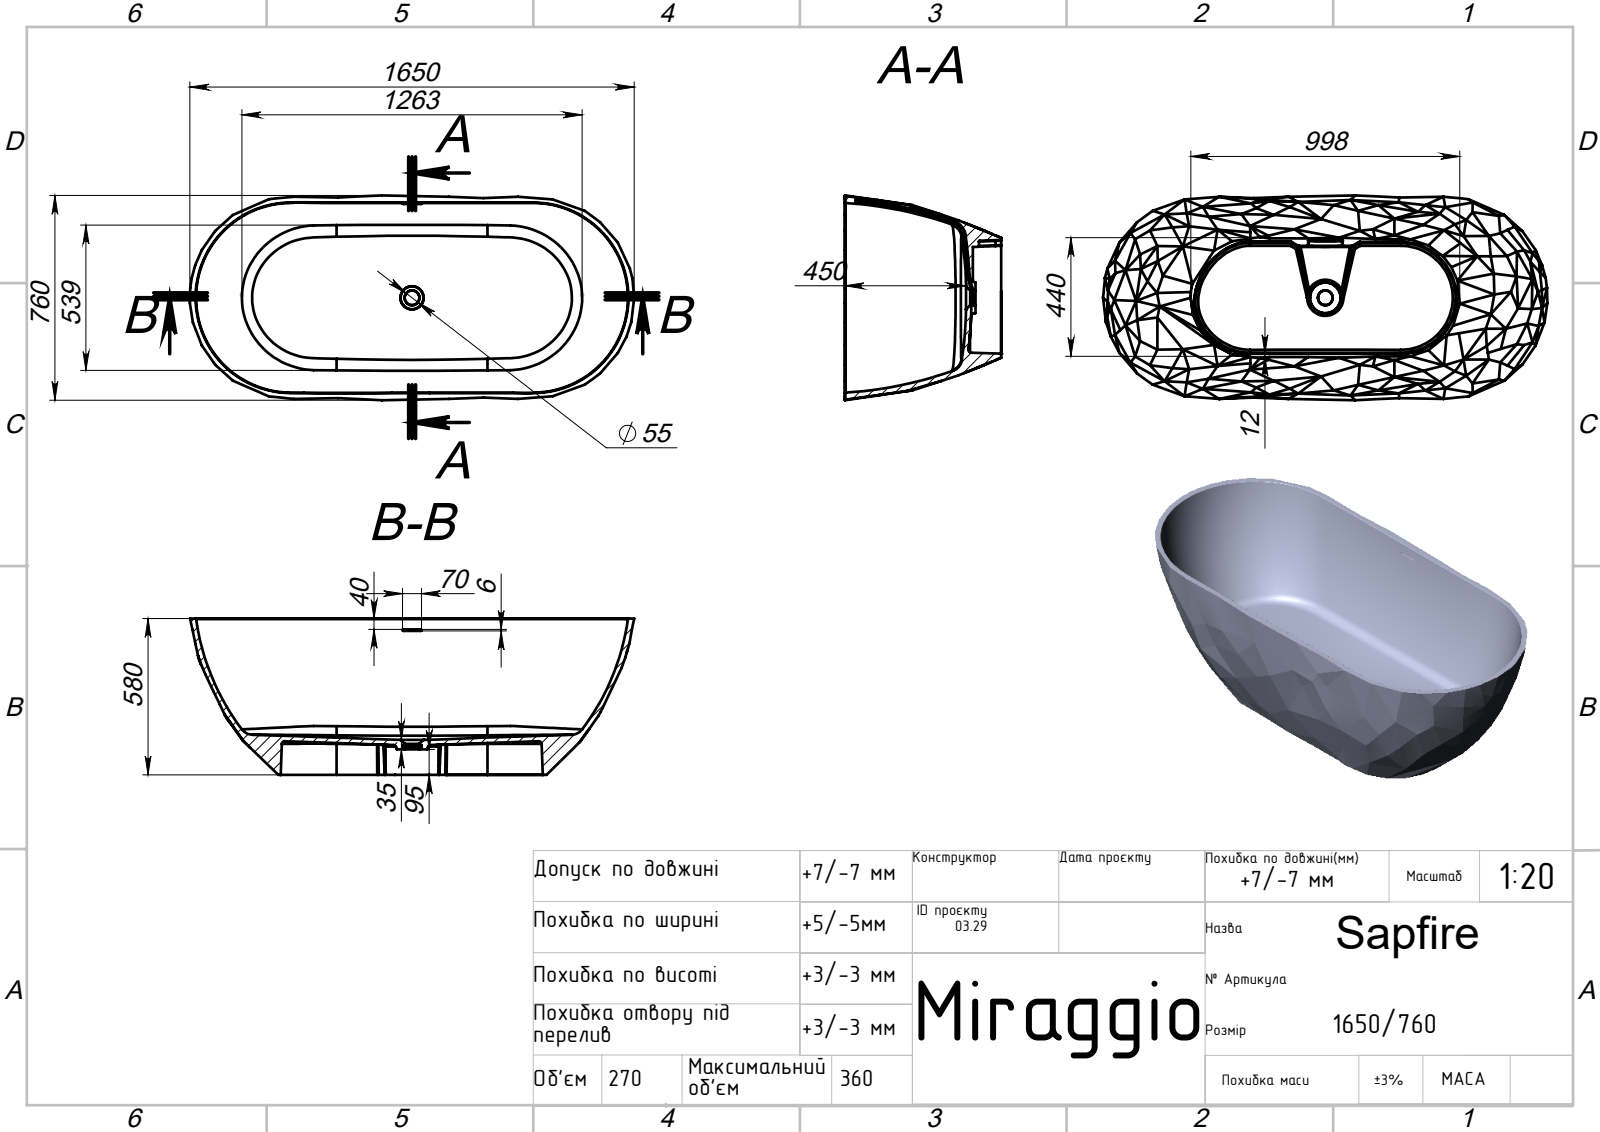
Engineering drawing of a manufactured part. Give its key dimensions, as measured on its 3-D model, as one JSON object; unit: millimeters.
{"part_name": "Sapfire", "step_written_by": "SolidWorks 2020 (AUTOMOTIVE_DESIGN)", "units": "millimeters", "bodies": {"solids": 1, "faces": 383, "planar": 234, "cylindrical": 20, "other": 129}, "overall_size": [1649.47, 760, 580], "volume_mm3": 63920000, "surface_area_mm2": 5275000, "round_holes": [[55, 1]], "partial_cylinders_radius": [[3, 6], [10, 6], [57, 1], [62.5, 1], [64, 1], [331.21, 1], [343.83, 1]], "face_to_face_distances": [580, 105, 475, 14.93, 21.99, 7.06, 95, 10, 485, 70]}
